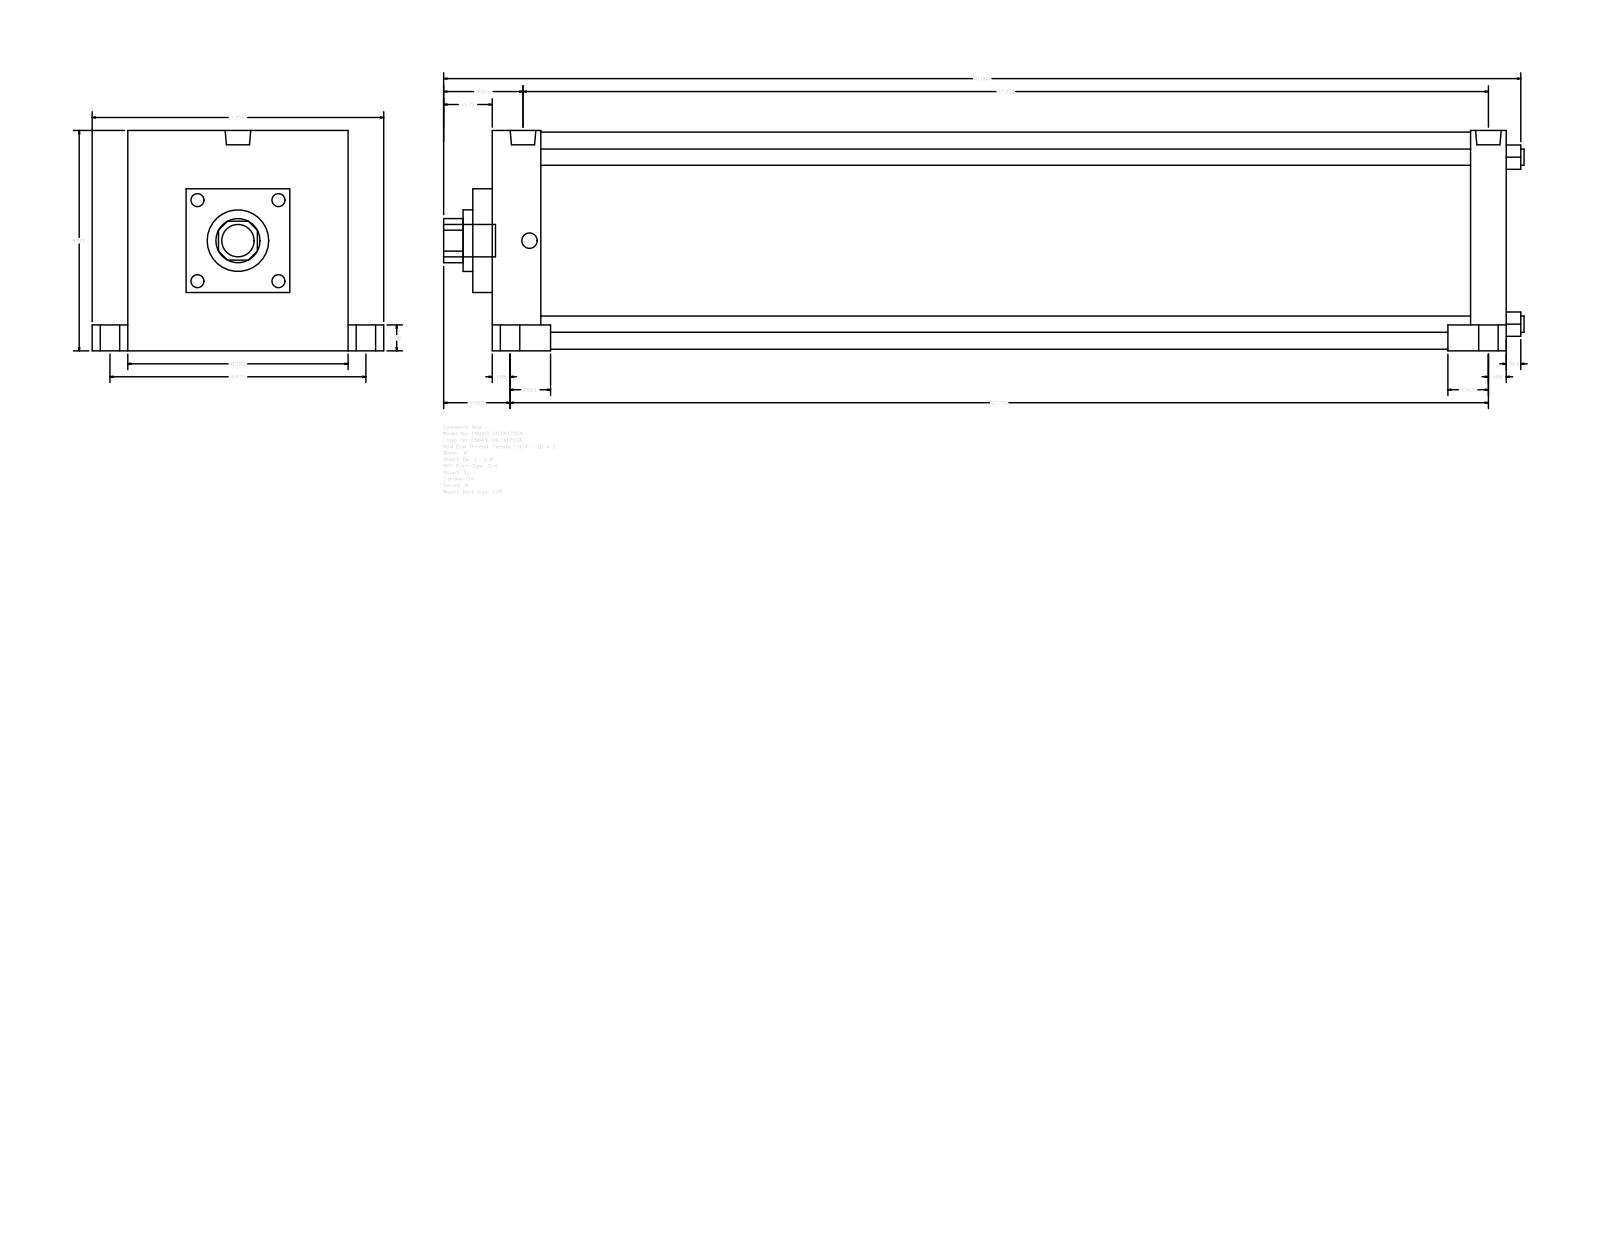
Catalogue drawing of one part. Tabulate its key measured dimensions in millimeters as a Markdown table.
| quantity | value |
| --- | --- |
| part name | A_SL__0800_1.75 |
| STEP written by | GSSL Pune (CONFIG_CONTROL_DESIGN) |
| units | millimeters |
| bodies | 0 solids, 117 faces (85 planar, 32 cylindrical, 0 other) |
| overall size | 1058.86 × 285.75 × 215.9 |
| round holes (diameter × count) | 15.88 × 4, 44.45 × 1, 60.33 × 1, 212.72 × 1 |
| round bosses / shafts (diameter × count) | 25.4 × 4, 19.05 × 4, 15.08 × 4, 25.12 × 2, 31.75 × 1 |
| partial cylindrical surfaces (radius × count) | 21.63 × 1 |
| main face-to-face distances | 993.78, 215.9, 34.92, 47.63, 946.15, 958.86, 911.23, 57.15, 19.05, 158.75 |
| hole center spacings | 115.67, 163.58, 231.34 |
